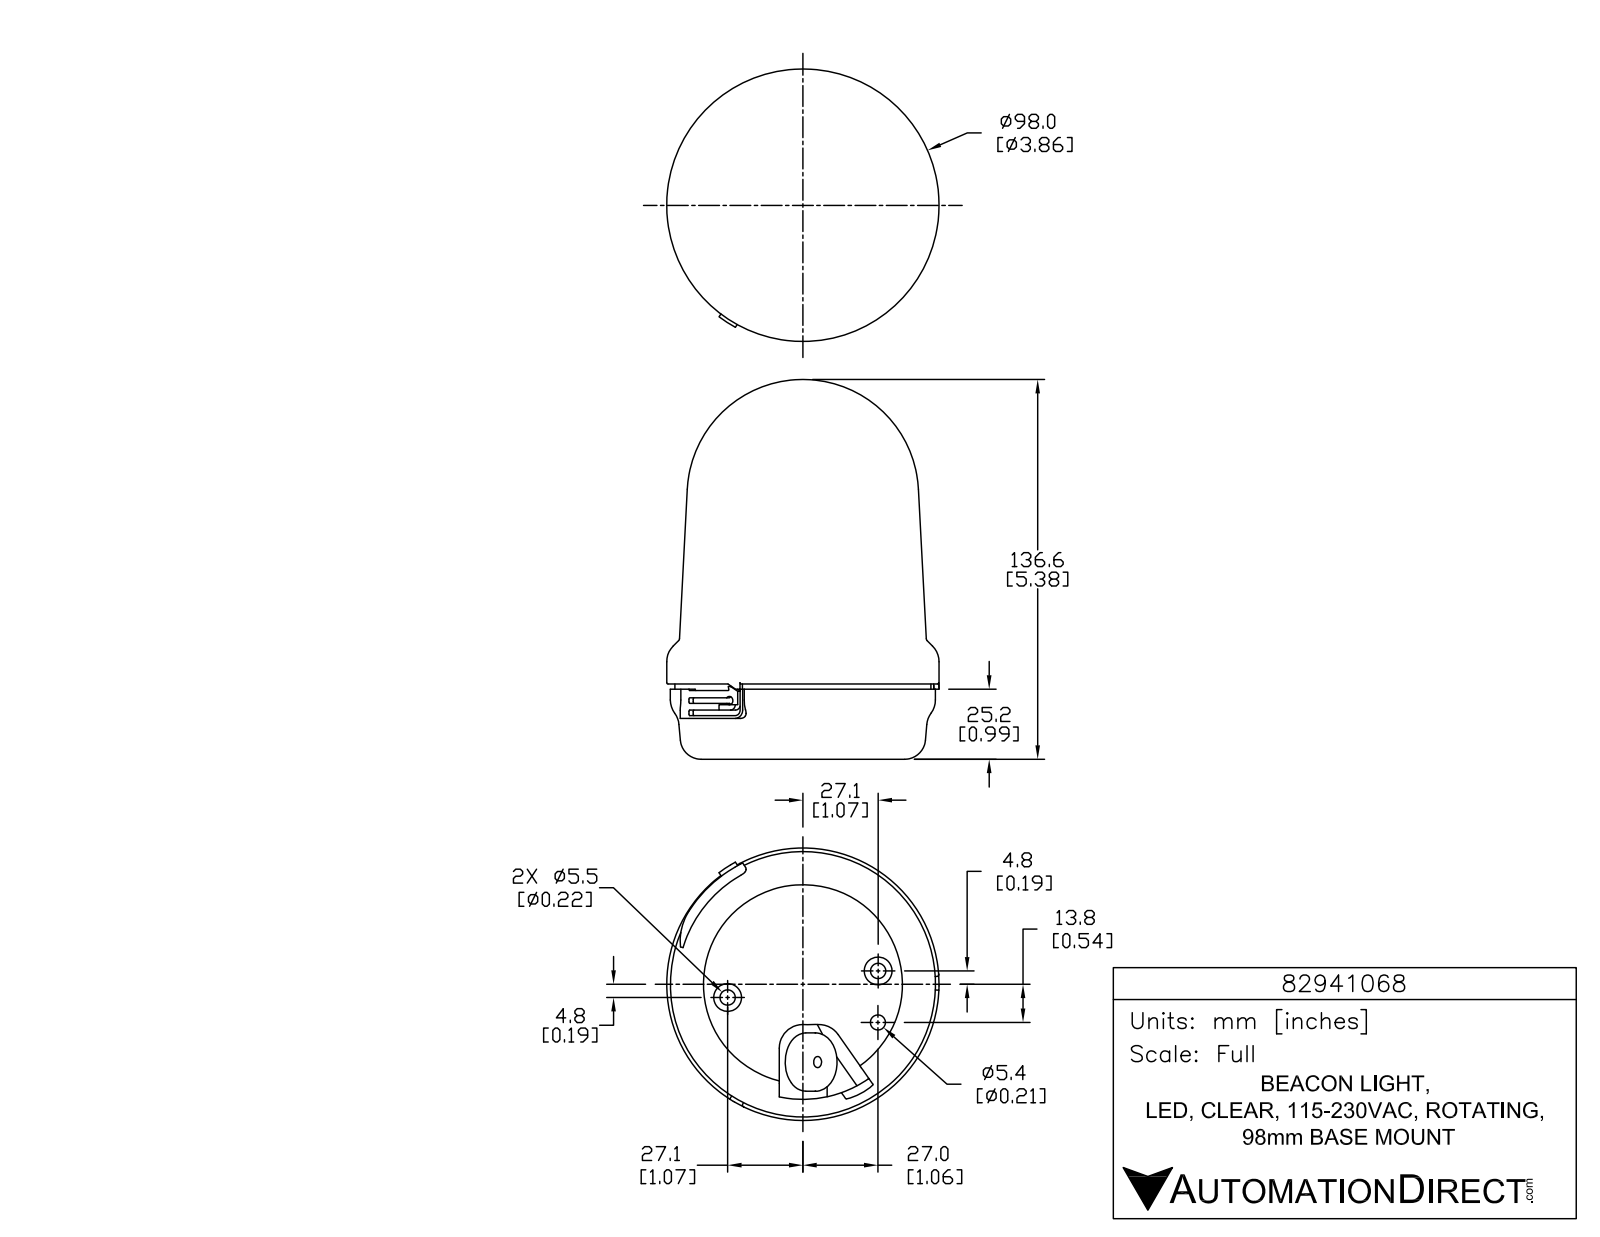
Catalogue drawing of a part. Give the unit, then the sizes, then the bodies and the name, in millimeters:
Units: millimetres
Overall size (bounding box): 136.6 × 98 × 98
Round holes (diameter × count): ⌀1.5 ×3, ⌀5.5 ×2, ⌀4 ×1, ⌀5.4 ×1, ⌀71.6 ×1
Round bosses / shafts (diameter × count): ⌀8.6 ×3, ⌀2.1 ×3, ⌀10 ×2, ⌀98 ×1, ⌀95.4 ×1, ⌀92.1 ×1, ⌀21 ×1
Partial cylindrical surfaces — rounded edges, fillets, slot ends (radius × count): R0.1 ×9, R0.1 ×6, R0.3 ×6, R0.3 ×6, R0.3 ×6, R5 ×6, R0.5 ×5, R1 ×4
Main face-to-face distances: 26.5, 24.7, 1.9, 0.5, 25.2, 27.1, 6, 14.7, 14.2, 10.5
Hole centre spacings: 27.5, 18.5, 30.3, 54.8, 55
Volume: 732 300 mm³ · Surface area: 47 520 mm²
Bodies: 1 solid, 872 faces (566 planar, 204 cylindrical, 102 other)
Part name (STEP PRODUCT): 82941068
STEP written by: SolidWorks 2015 (AUTOMOTIVE_DESIGN)
